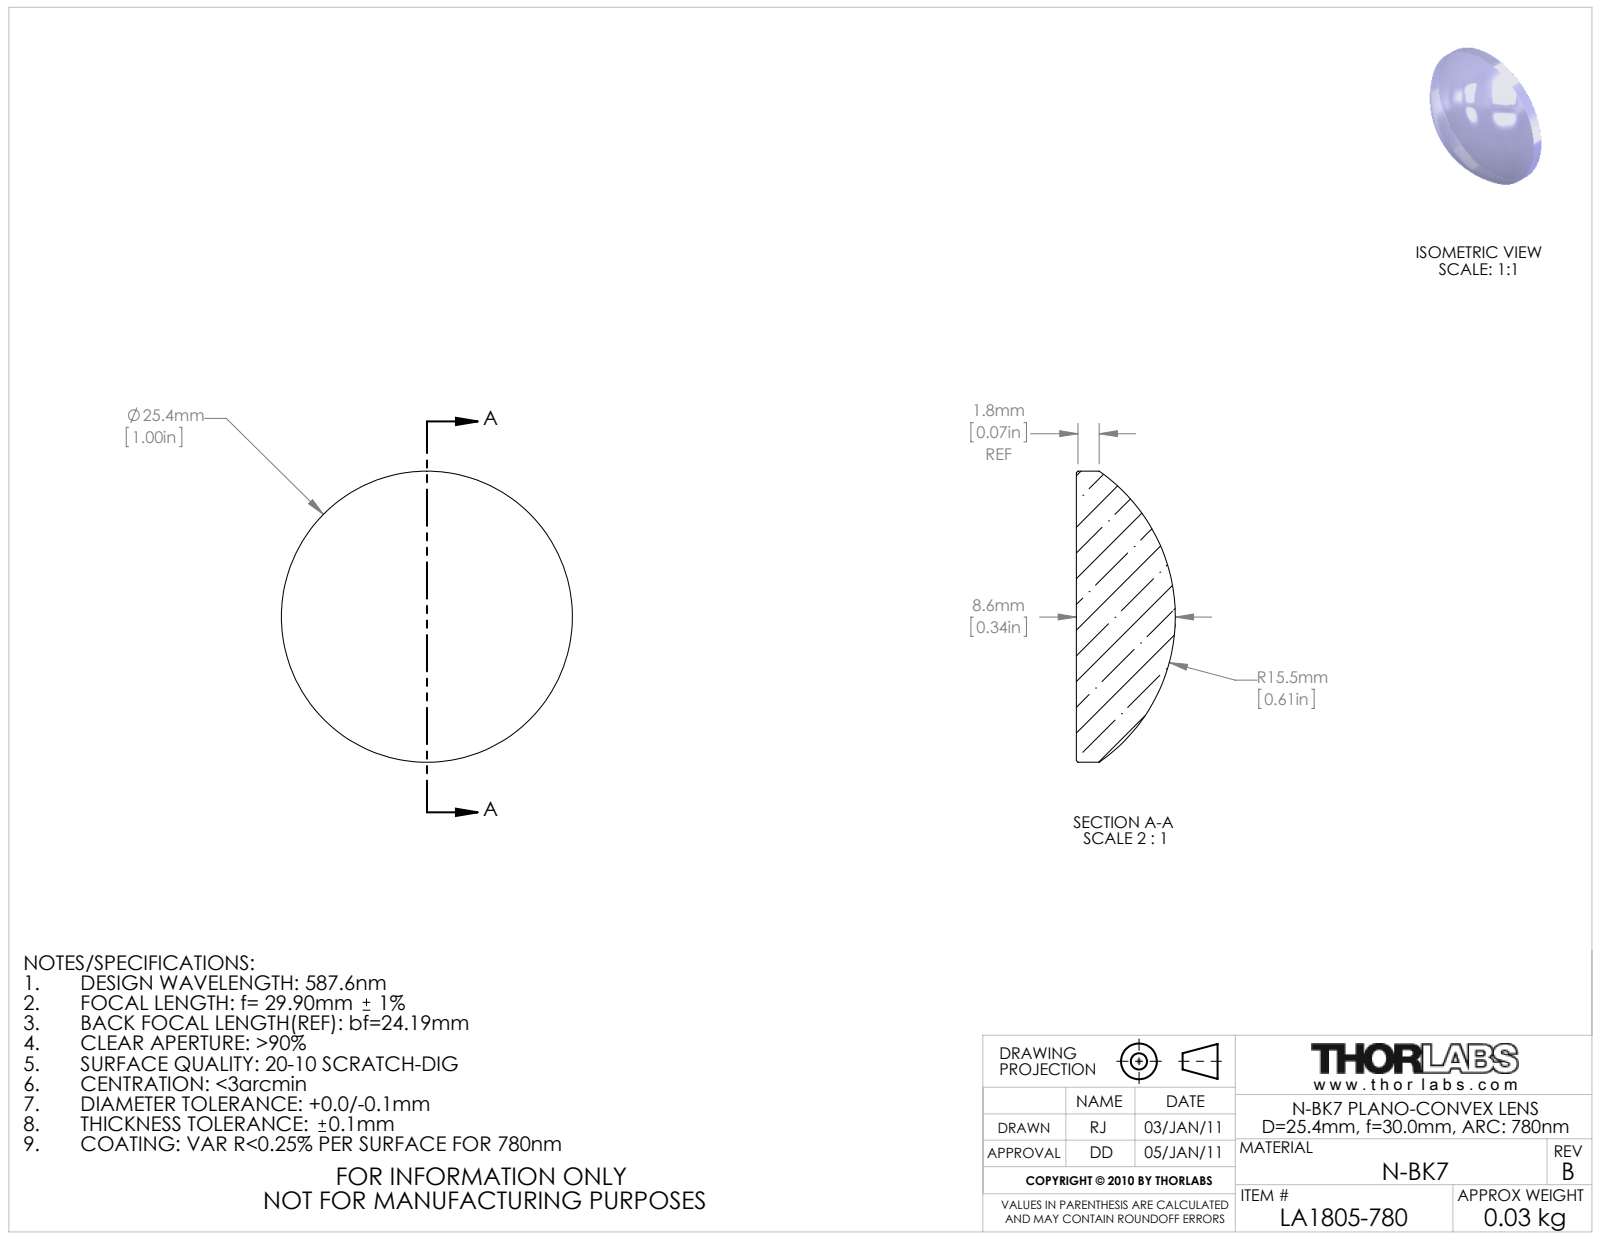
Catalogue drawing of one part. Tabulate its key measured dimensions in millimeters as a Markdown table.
| quantity | value |
| --- | --- |
| part name | 21784-E0W |
| STEP written by | SolidWorks 2011 (AUTOMOTIVE_DESIGN) |
| units | millimeters |
| bodies | 0 solids, 7 faces (1 planar, 2 cylindrical, 4 other) |
| overall size | 25.4 × 25.4 × 8.64 |
| round bosses / shafts (diameter × count) | 25.4 × 1 |
